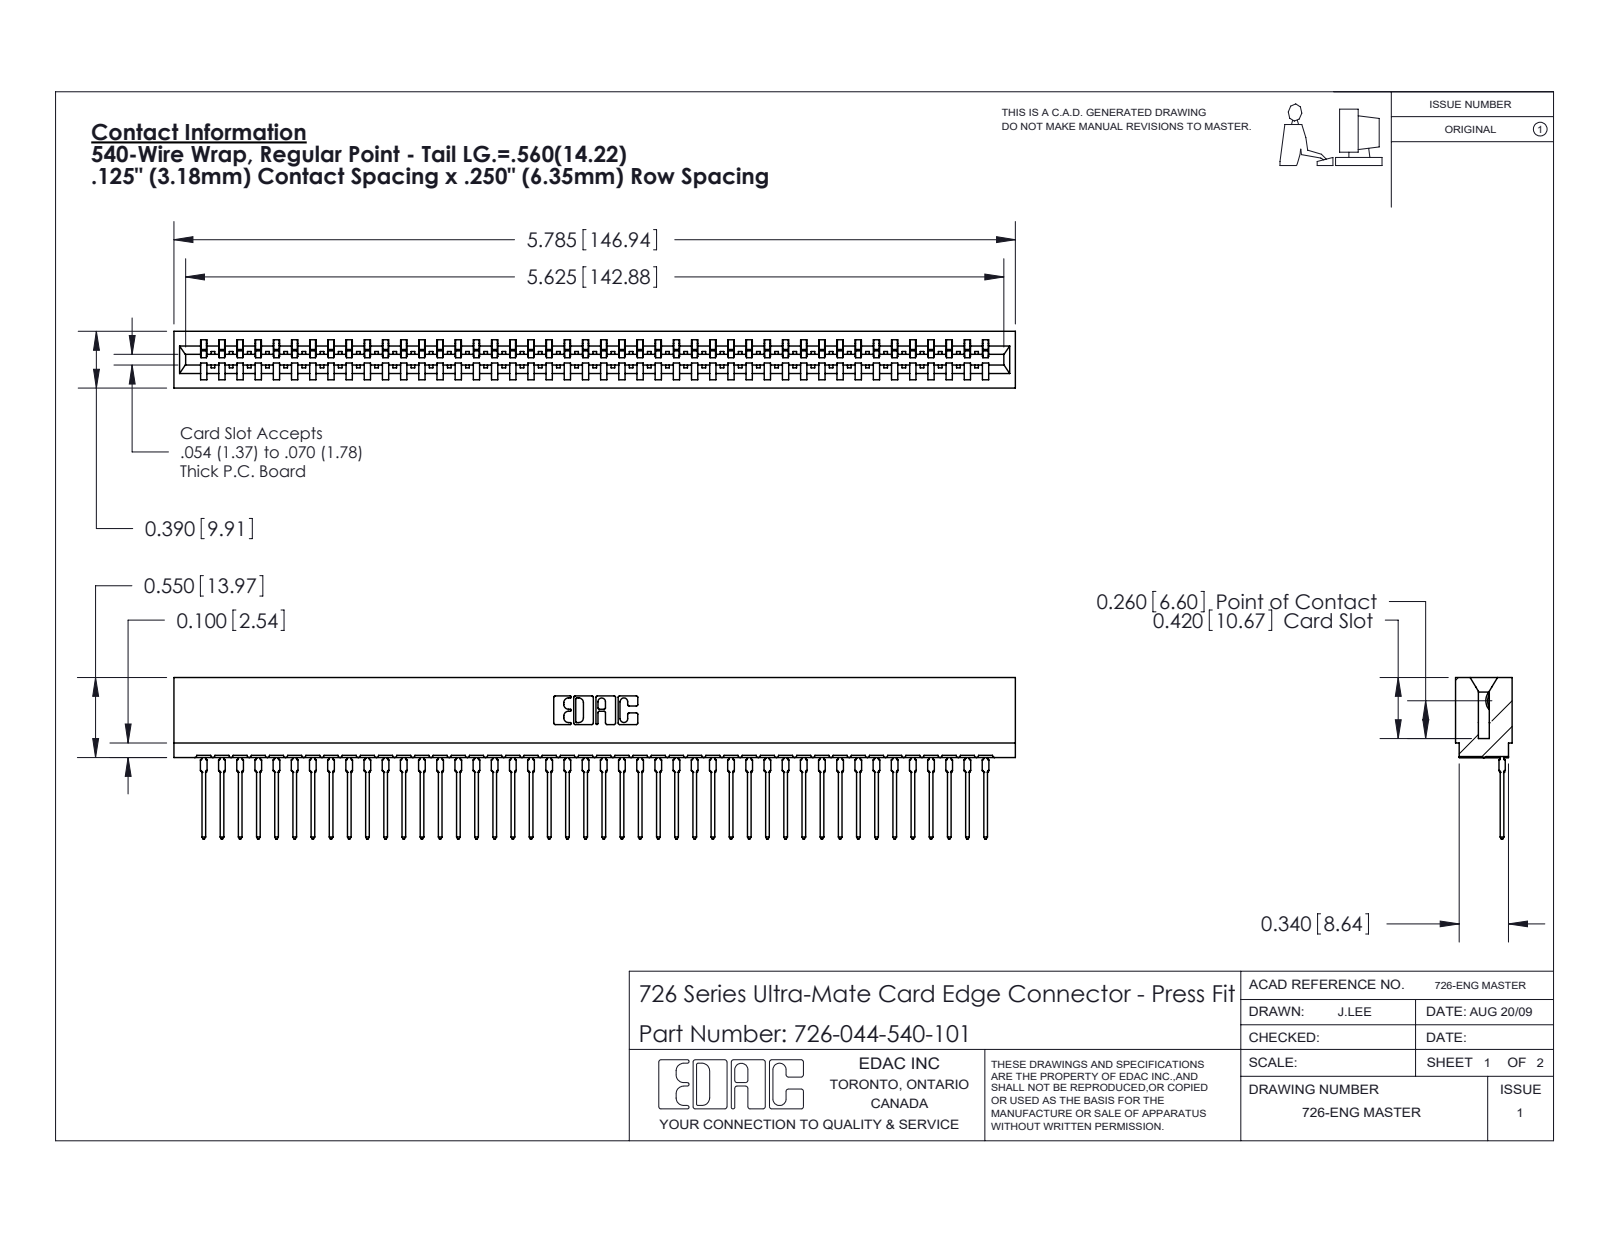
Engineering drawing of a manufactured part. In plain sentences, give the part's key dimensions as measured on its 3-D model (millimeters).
The part is named "726-044-540-101; 726 Part_.515 Slot Depth - 01; 746-292-001_540". Its 3-D file was written by "SolidWorks 2020 (CONFIG_CONTROL_DESIGN)". It is 45 solids with 4849 faces: 2827 planar, 878 cylindrical and 1144 other. Overall it measures 146.9 by 28.2 by 9.9 millimeters. Its volume is 13 200 cubic millimeters and its surface area 20 720 square millimeters. Partial cylindrical surfaces (rounded edges, fillets, slot ends): 88 of radius 0.5, 45 of radius 0.4, 22 of radius 0.3, 6 of radius 0.2, 6 of radius 0.8, 4 of radius 0.1, 4 of radius 0.3, 3 of radius 0.7. The main face-to-face distances are 1.4, 8.5, 9.9, 0.6, 7.8, 6.4, 2.1, 7, 9.3, 0.8.
